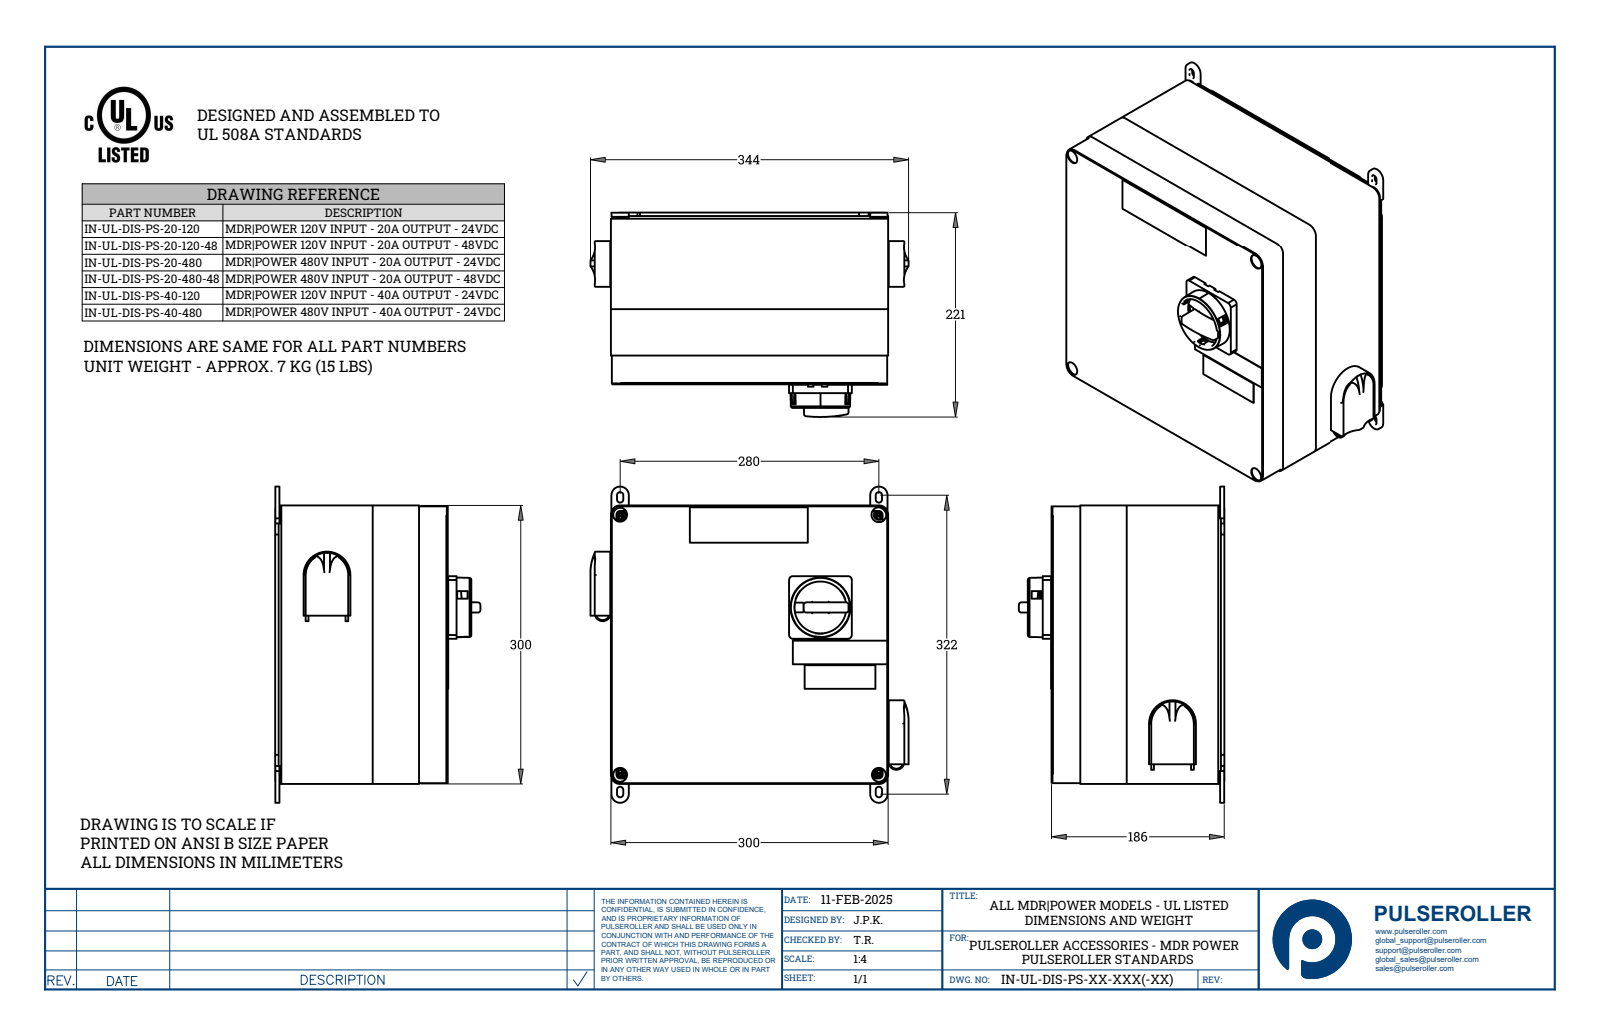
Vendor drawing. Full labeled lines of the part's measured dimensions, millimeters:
Part name (STEP PRODUCT): IN-UL-DIS-PS-xx-xxx(-xx) v4; aMDRPowerSupplyBack v2; aSidePieceUL v2; aSidePieceMount v3
STEP written by: Autodesk Translation Framework v13.20.0.188 (AP242_MANAGED_MODEL_BASED_3D_ENGINEERING_MIM_LF)
Units: millimetres
Bodies: 15 solids, 1659 faces (952 planar, 419 cylindrical, 288 other)
Overall size (bounding box): 344 × 340.57 × 221.25
Volume: 1 689 000 mm³ · Surface area: 923 357 mm²
Round holes (diameter × count): ⌀4 ×8, ⌀3.2 ×6, ⌀4.3 ×6, ⌀2.6 ×4, ⌀2.9 ×4, ⌀17.9 ×4, ⌀15 ×3, ⌀28.2 ×2, ⌀28.57 ×2, ⌀16 ×1, ⌀23 ×1
Round bosses / shafts (diameter × count): ⌀9 ×6, ⌀34.5 ×2, ⌀28 ×2
Partial cylindrical surfaces — rounded edges, fillets, slot ends (radius × count): R0.3 ×18, R0.5 ×13, R0.73 ×8, R1 ×8, R1.2 ×8, R2.5 ×8, R3.7 ×8, R4.6 ×8
Main face-to-face distances: 6, 294, 1, 179.5, 178.5, 300, 288, 5.75, 185.25, 184.25
Hole centre spacings: 20.59, 280, 20.6, 19.8, 20.62, 20.88, 35.49, 35.5
